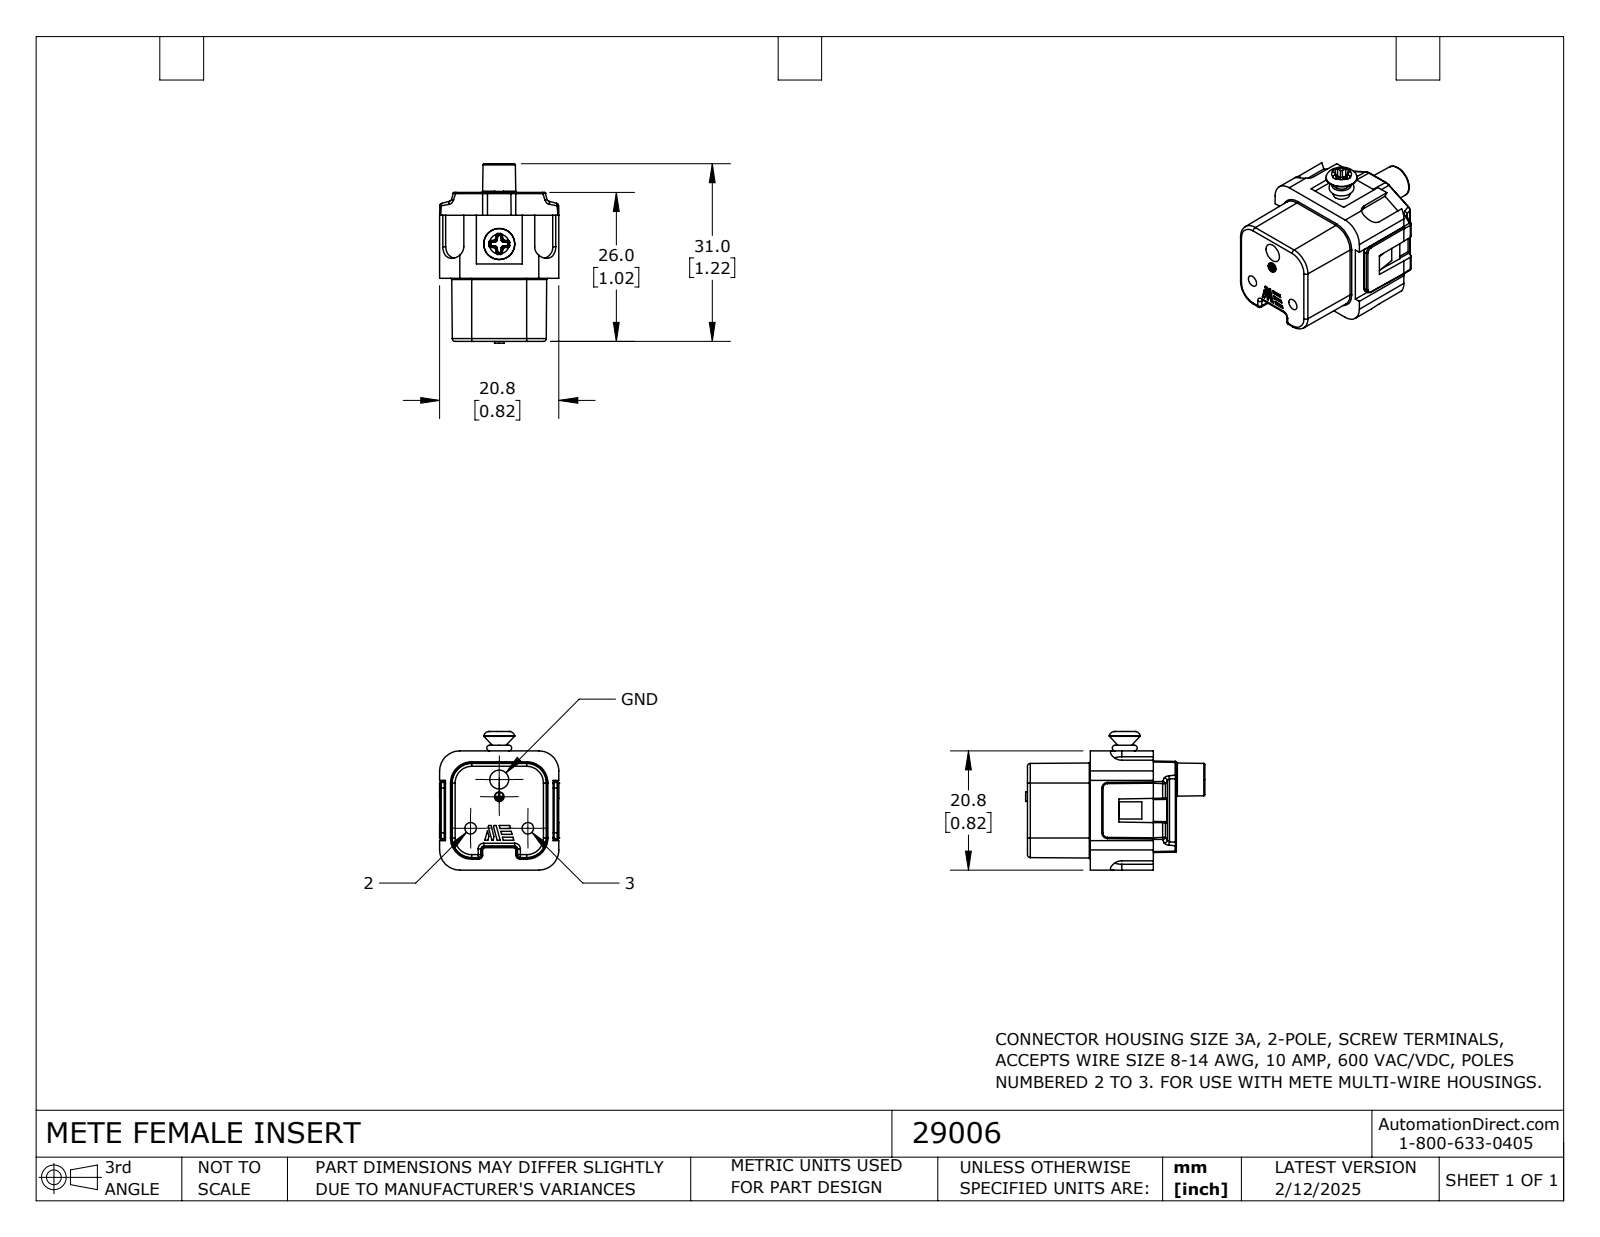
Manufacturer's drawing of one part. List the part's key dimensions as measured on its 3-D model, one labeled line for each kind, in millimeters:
Part name (STEP PRODUCT): 29006
STEP written by: SolidWorks 2024 (CONFIG_CONTROL_DESIGN)
Units: millimetres
Bodies: 1 solid, 464 faces (196 planar, 141 cylindrical, 127 other)
Overall size (bounding box): 31.3 × 24.2 × 20.8
Volume: 7 654 mm³ · Surface area: 3 714 mm²
Round holes (diameter × count): ⌀2 ×2, ⌀1.54 ×1, ⌀3.3 ×1
Round bosses / shafts (diameter × count): ⌀2.87 ×1, ⌀1.65 ×1
Partial cylindrical surfaces — rounded edges, fillets, slot ends (radius × count): R0.2 ×37, R0.5 ×21, R0.1 ×12, R0.3 ×12, R2 ×9, R0.4 ×4, R3.5 ×4, R2.5 ×3
Main face-to-face distances: 11, 2, 22, 1, 4, 19.8, 15, 20.8, 26, 21.84
Hole centre spacings: 7.43, 9.86, 3, 10
